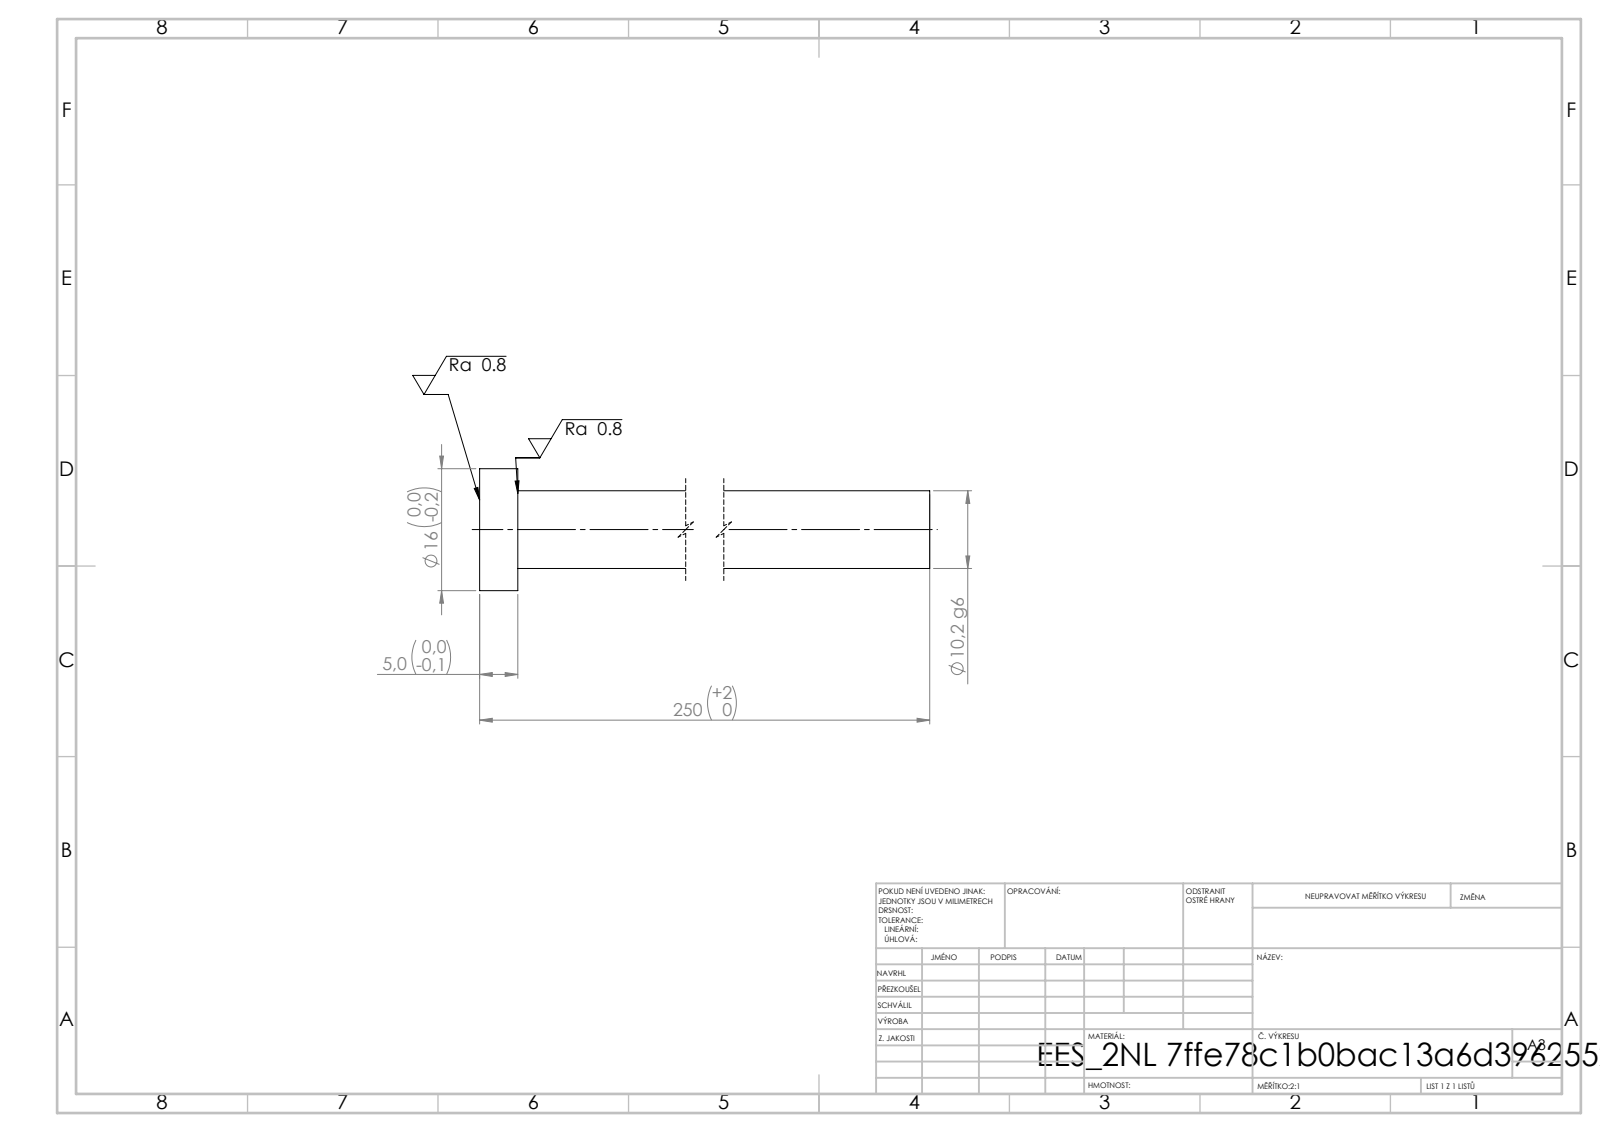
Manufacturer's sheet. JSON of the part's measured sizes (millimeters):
{"step_written_by": "SolidWorks 2019 (CONFIG_CONTROL_DESIGN)", "units": "millimeters", "bodies": {"solids": 1, "faces": 7, "planar": 3, "cylindrical": 4, "other": 0}, "overall_size": [250, 16, 16], "volume_mm3": 21025, "surface_area_mm2": 8504, "round_bosses_or_shafts": [[16, 1], [10.2, 1]], "face_to_face_distances": [5, 250, 245]}
